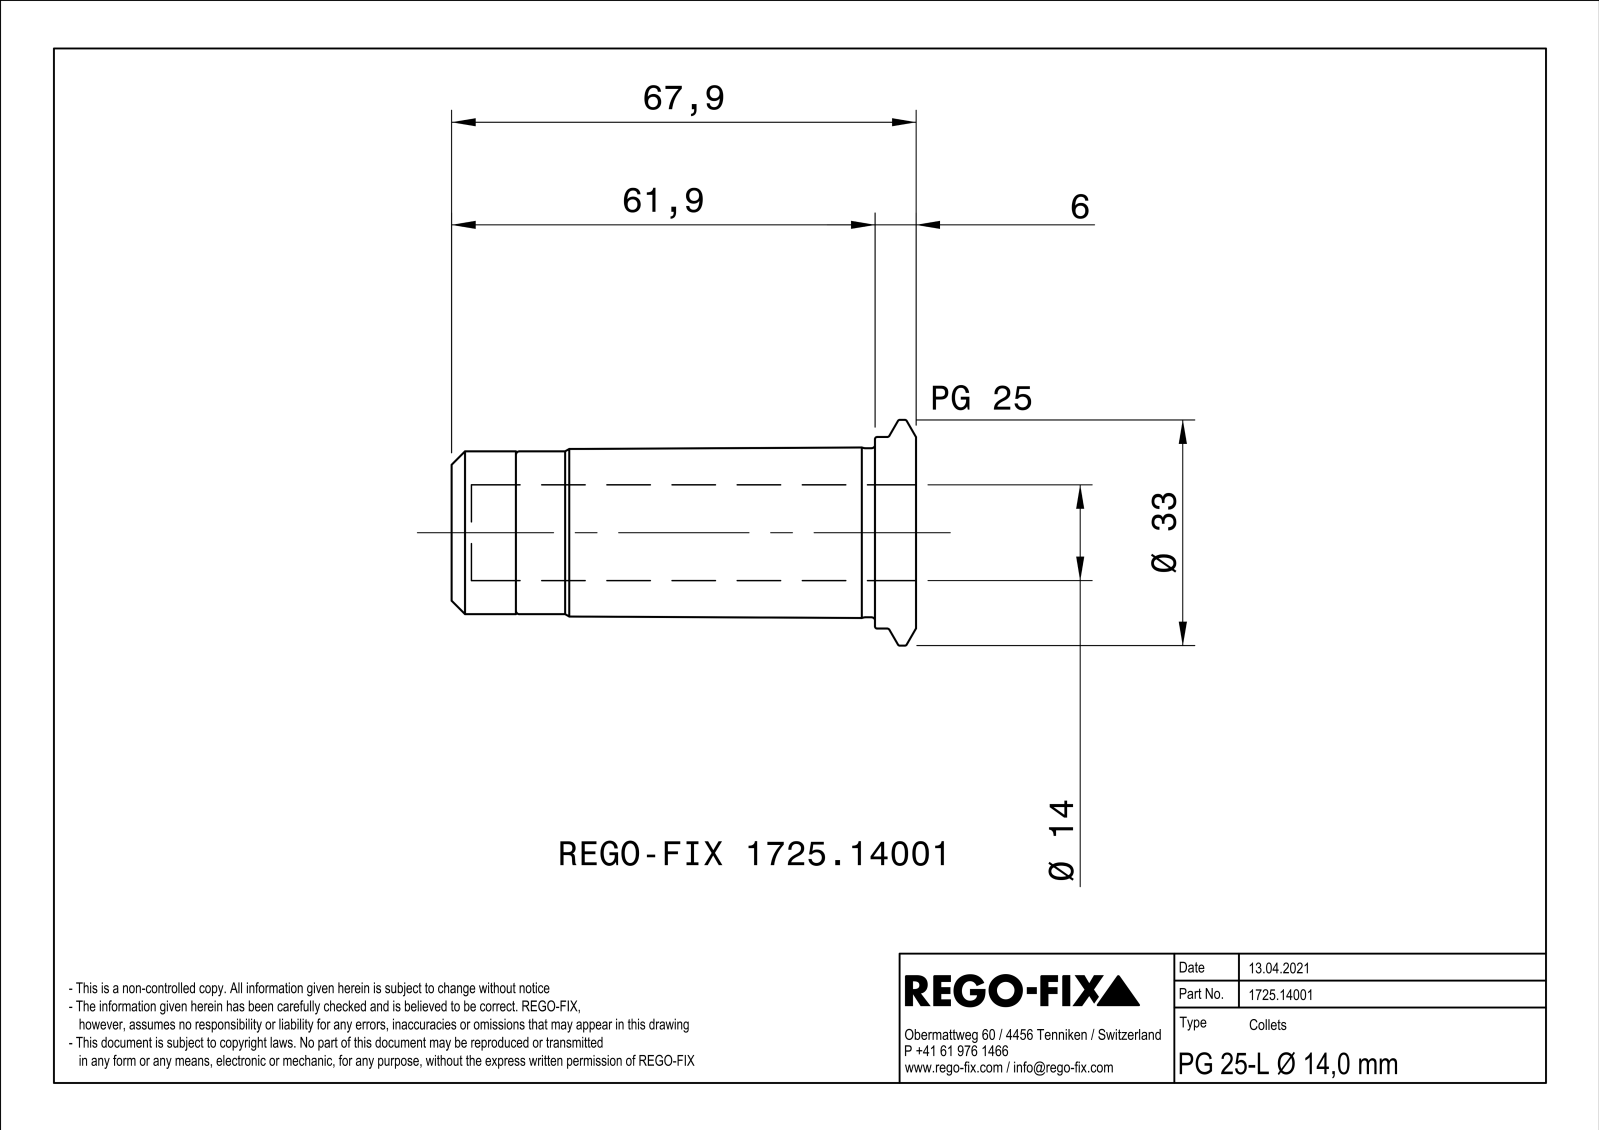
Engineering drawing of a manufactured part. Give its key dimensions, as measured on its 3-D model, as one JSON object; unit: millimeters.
{"part_name": "NOCUT", "step_written_by": "SIEMENS PLM Software Solid Edge ST10 (AUTOMOTIVE_DESIGN)", "units": "millimeters", "bodies": {"solids": 1, "faces": 93, "planar": 29, "cylindrical": 21, "other": 43}, "overall_size": [67.9, 33, 32.99], "round_holes": [[2.8, 1], [14, 1], [18.5, 1], [20.4, 1], [22.2, 1]], "round_bosses_or_shafts": [[33, 1], [28, 1], [24.7, 1], [23.8, 1], [22, 1], [20.92, 1]], "partial_cylinders_radius": [[2, 3]], "face_to_face_distances": [1, 67.9, 51, 16.9, 6, 52.5, 45, 61.9, 58.5, 7.5]}
